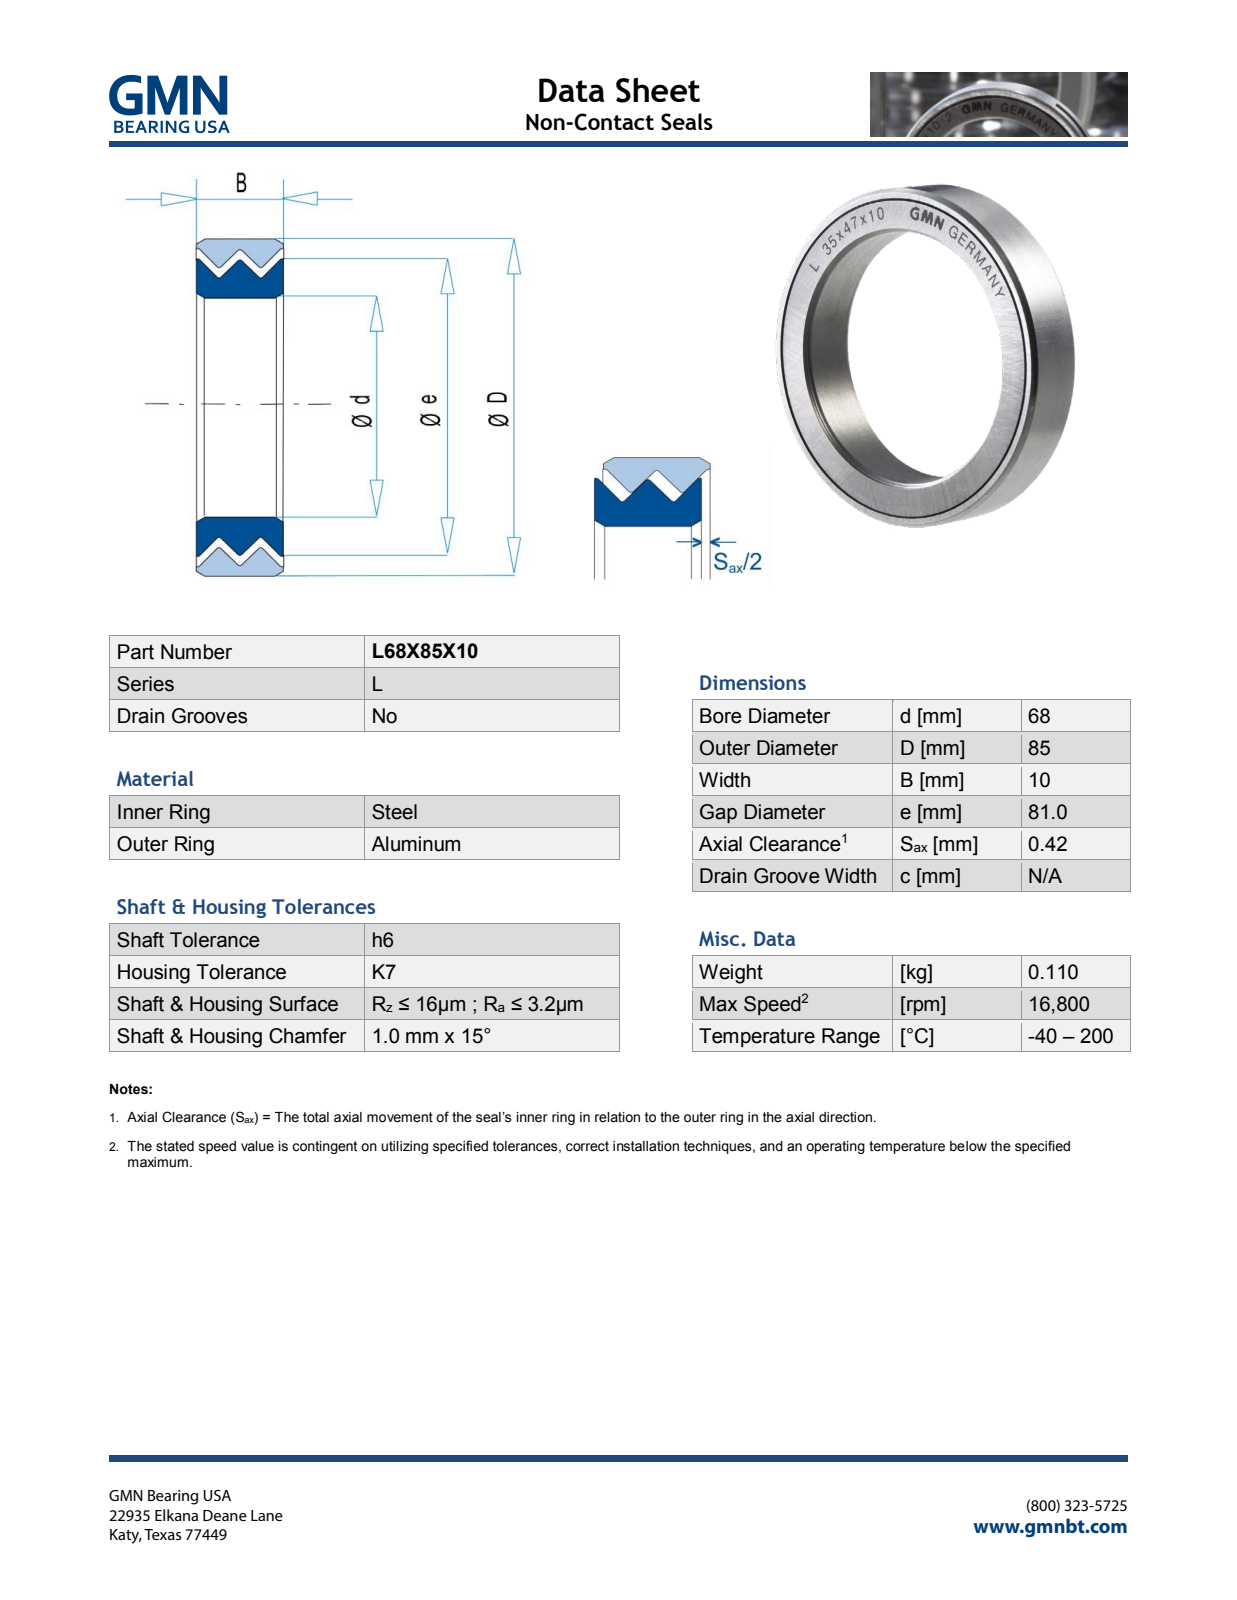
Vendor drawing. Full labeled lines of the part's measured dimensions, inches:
Part name (STEP PRODUCT): L68X85X10_PRT
STEP written by: PRO/ENGINEER BY PARAMETRIC TECHNOLOGY CORPORATION, 2013150 (AUTOMOTIVE_DESIGN)
Units: inches
Bodies: 2 solids, 662 faces (606 planar, 12 cylindrical, 44 other)
Overall size (bounding box): 3.346 × 3.346 × 0.396
Volume: 1.2 in³ · Surface area: 23.37 in²
Round holes (diameter × count): ⌀2.677 ×1, ⌀3.201 ×1
Round bosses / shafts (diameter × count): ⌀3.346 ×1, ⌀3.189 ×1
Main face-to-face distances: 0.394, 0.396, 0.019, 0.154, 0.135, 0.02, 0.116, 0.017, 0.017, 0.135
